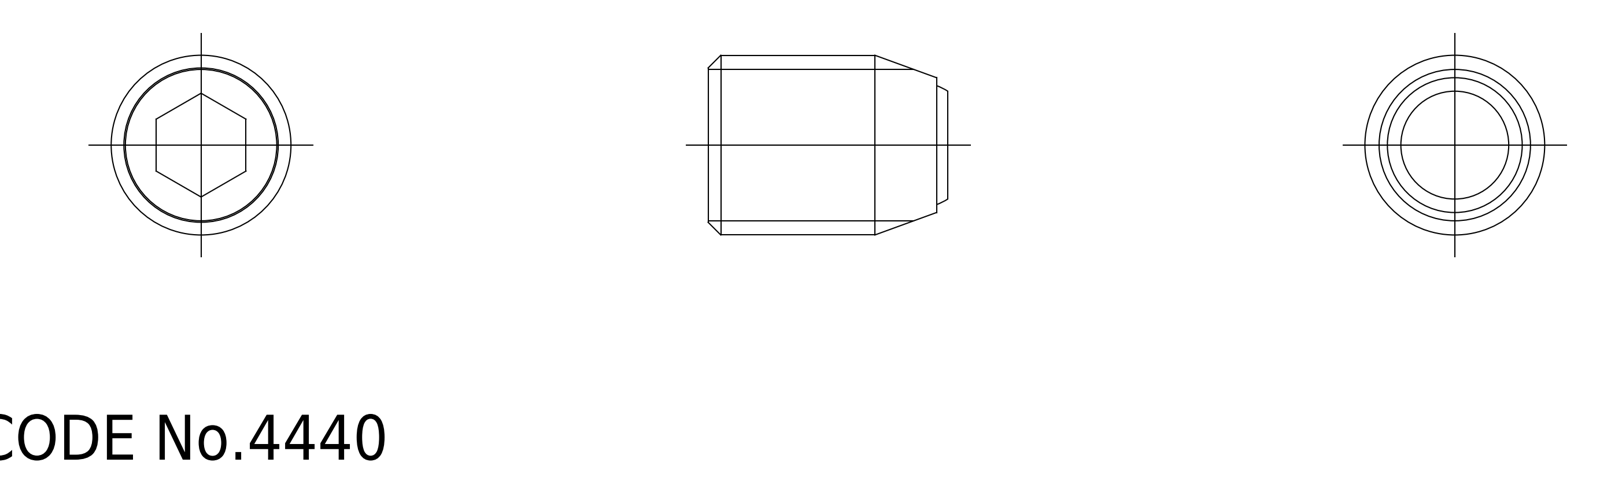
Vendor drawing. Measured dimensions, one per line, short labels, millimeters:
name: ball; SCS_M12_16_F_16010_36
written by: CADfix (AUTOMOTIVE_DESIGN)
unit: mm
bodies: 2 solids, 20 faces (0 planar, 0 cylindrical, 20 other)
size: 16.86 × 12 × 12
volume: 1 281 mm³; area: 1 266 mm²
